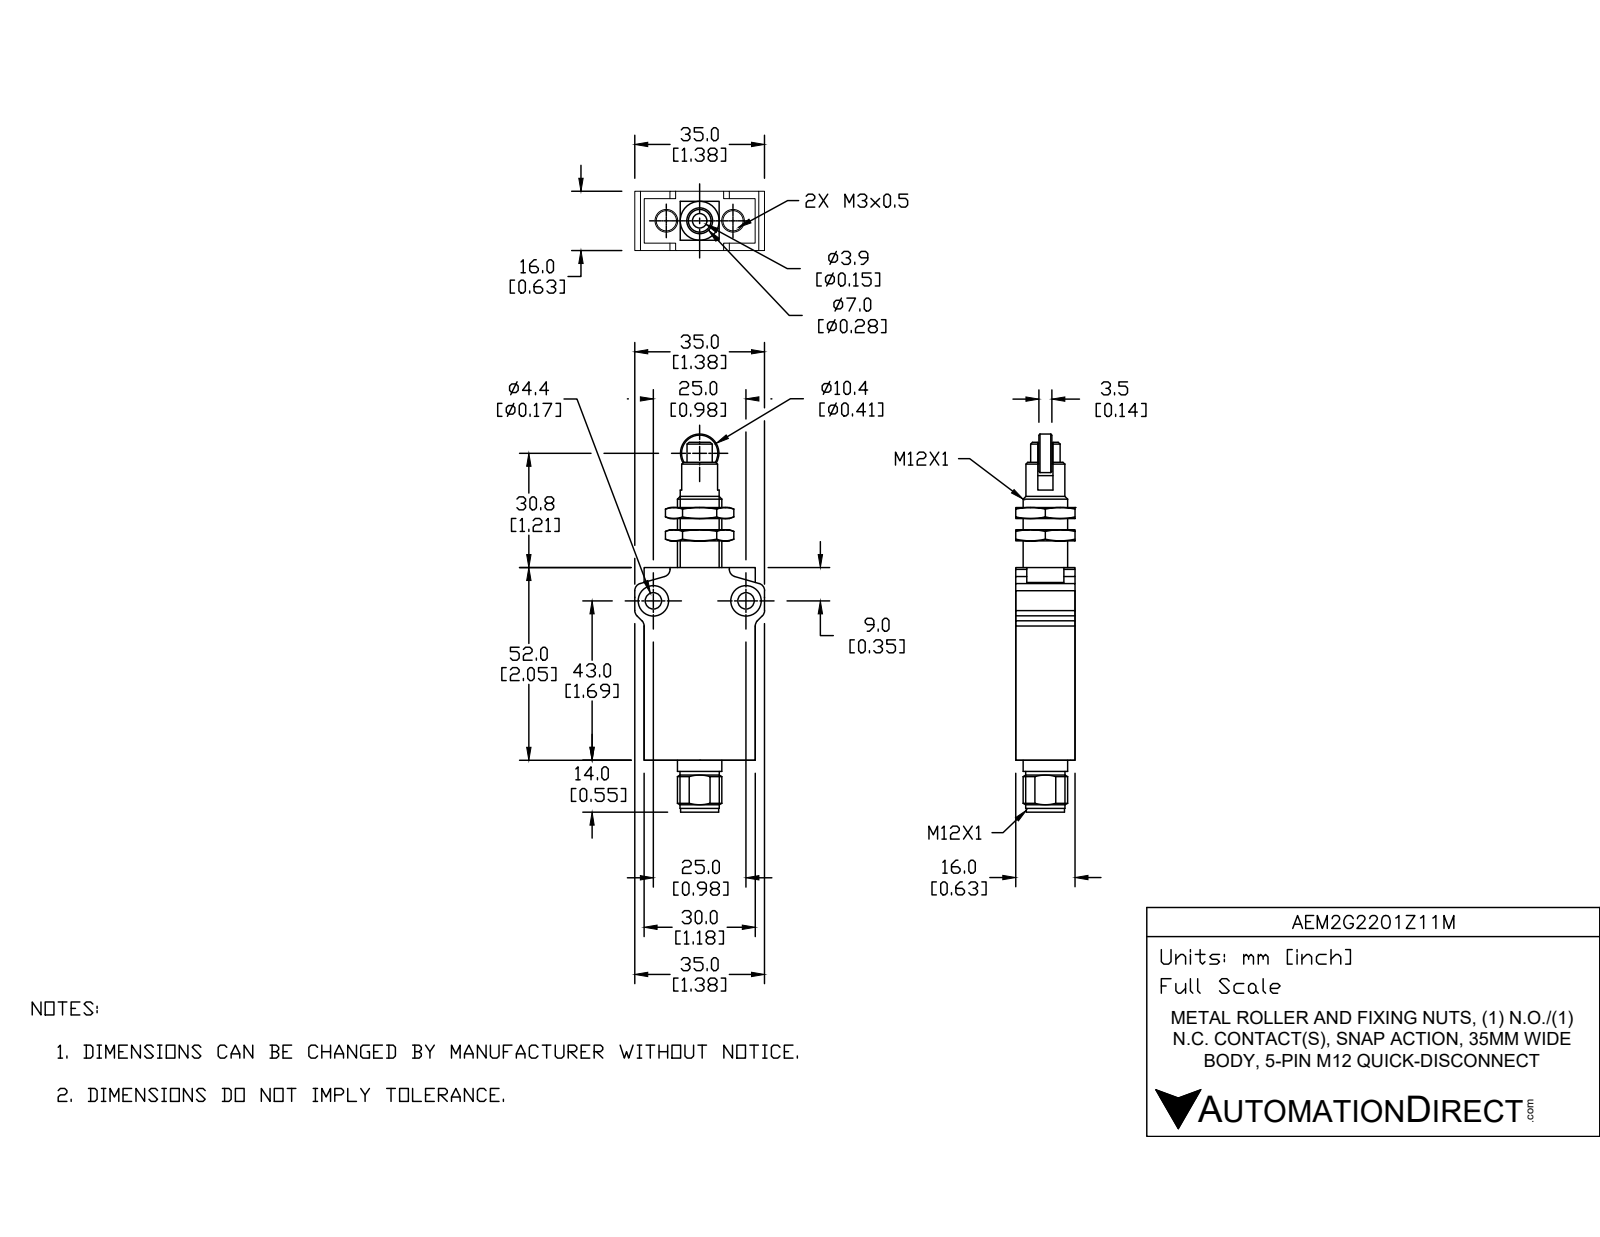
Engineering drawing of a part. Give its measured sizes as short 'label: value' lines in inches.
name: AEM2G2201Z11M
written by: SolidWorks 2017 (AUTOMOTIVE_DESIGN)
unit: in
bodies: 6 solids, 229 faces (82 planar, 76 cylindrical, 71 other)
size: 4.016 × 1.378 × 0.63
volume: 1.785 in³; area: 18.07 in²
holes: 2× ⌀0.118, 2× ⌀0.173, 2× ⌀0.323, 1× ⌀0.317
bosses: 1× ⌀0.472, 1× ⌀0.417, 1× ⌀0.413, 1× ⌀0.409, 1× ⌀0.406, 1× ⌀0.313, 1× ⌀0.22
rounds: 8× R0.079, 1× R0.256
face distances: 0.63, 1.181, 0.472, 0.118, 0.236, 2.047, 1.858, 0.189, 0.354, 0.234
hole spacings: 0.374, 0.748, 0.984
